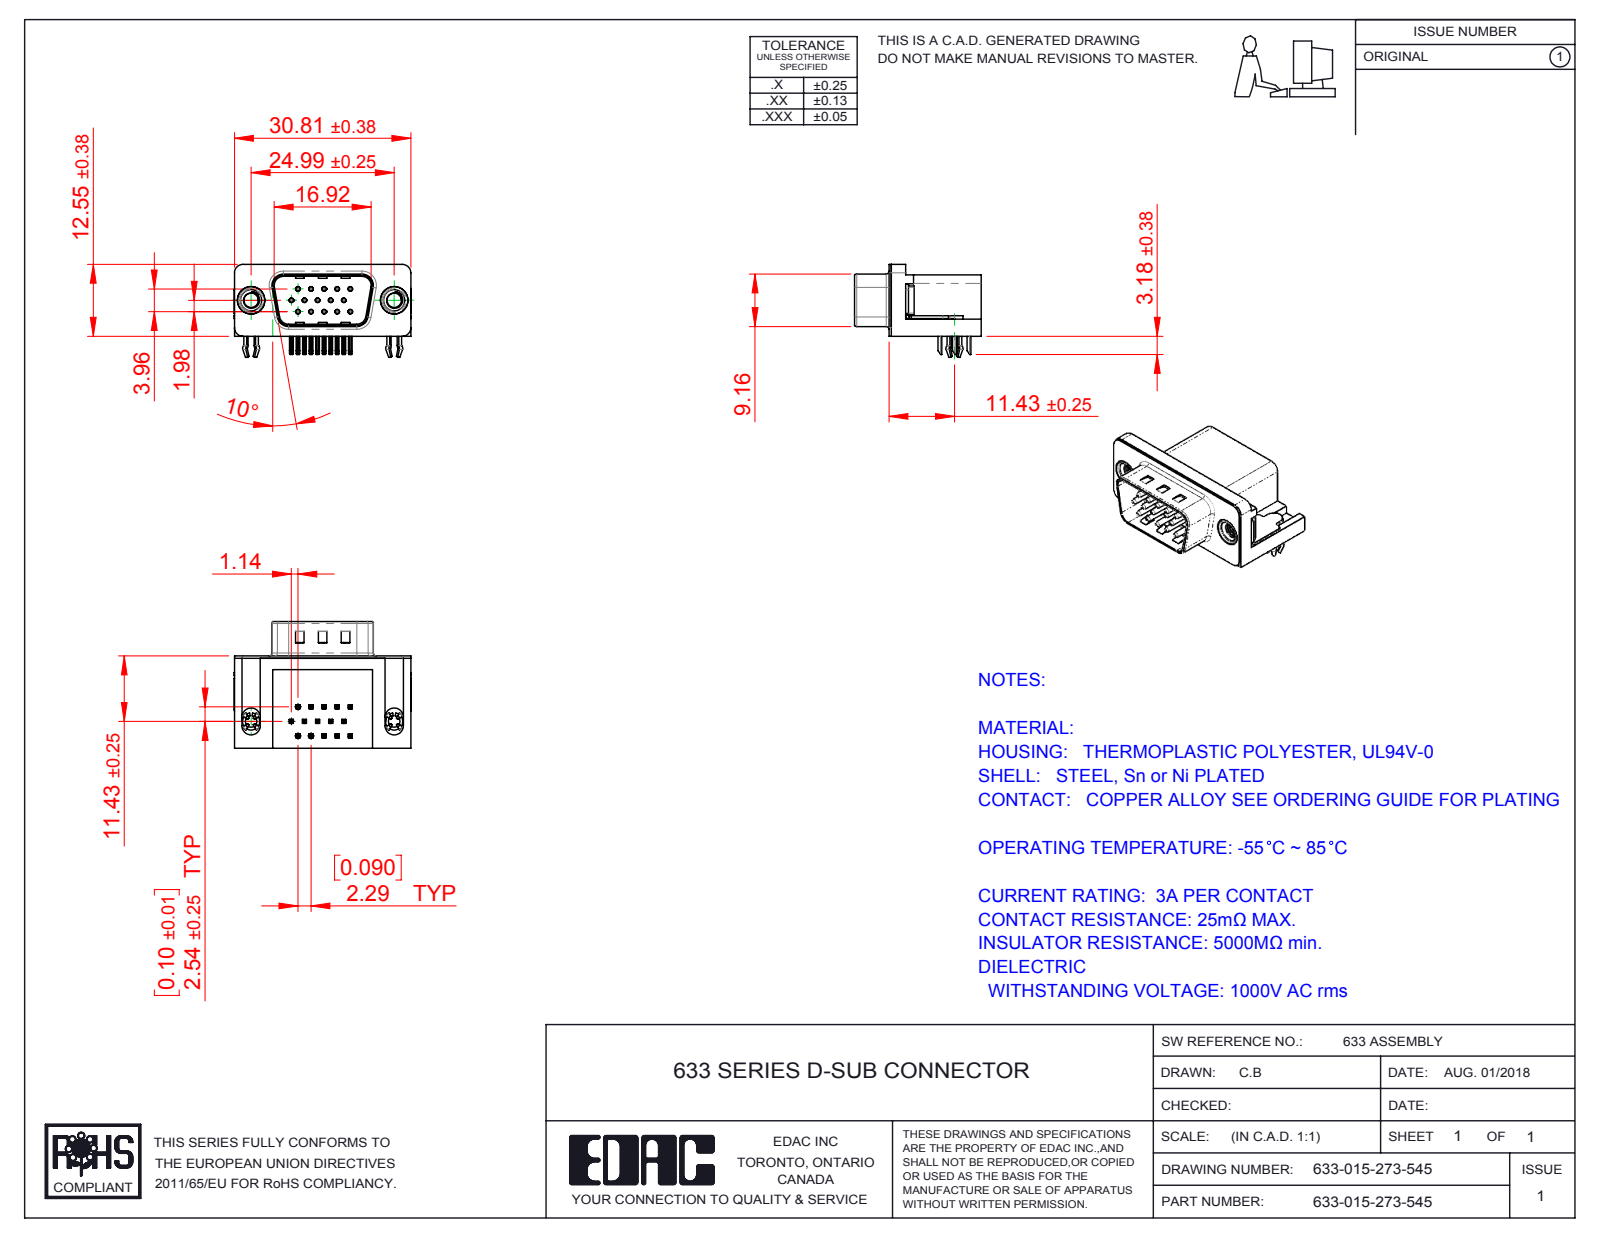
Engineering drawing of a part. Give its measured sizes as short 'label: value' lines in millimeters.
name: 633 Contact Middle; 633 Shell_15 Contact; 633-015-273-545; 633 4 Prong Board Lock (+5 more)
written by: SolidWorks 2016 (CONFIG_CONTROL_DESIGN)
unit: mm
bodies: 21 solids, 1563 faces (903 planar, 453 cylindrical, 207 other)
size: 30.89 × 22.1 × 16.25
volume: 4 077 mm³; area: 5 499 mm²
holes: 15× ⌀0.35, 15× ⌀0.8, 2× ⌀2, 2× ⌀2.5, 2× ⌀4, 2× ⌀4.8, 2× ⌀5
bosses: 15× ⌀0.75, 2× ⌀4.9, 2× ⌀4.75, 2× ⌀3.9, 2× ⌀3
rounds: 72× R0.25, 30× R0.12, 16× R1, 9× R0.5, 8× R1.6, 7× R1.5, 4× R0.9, 4× R2
face distances: 0.4, 10.35, 15.7, 2.9, 6.7, 16.1, 2.5, 0.5, 0.35, 10.7
hole spacings: 3.96, 2.28, 4.57, 2.29, 6.05, 6.86, 7.92, 6.04
